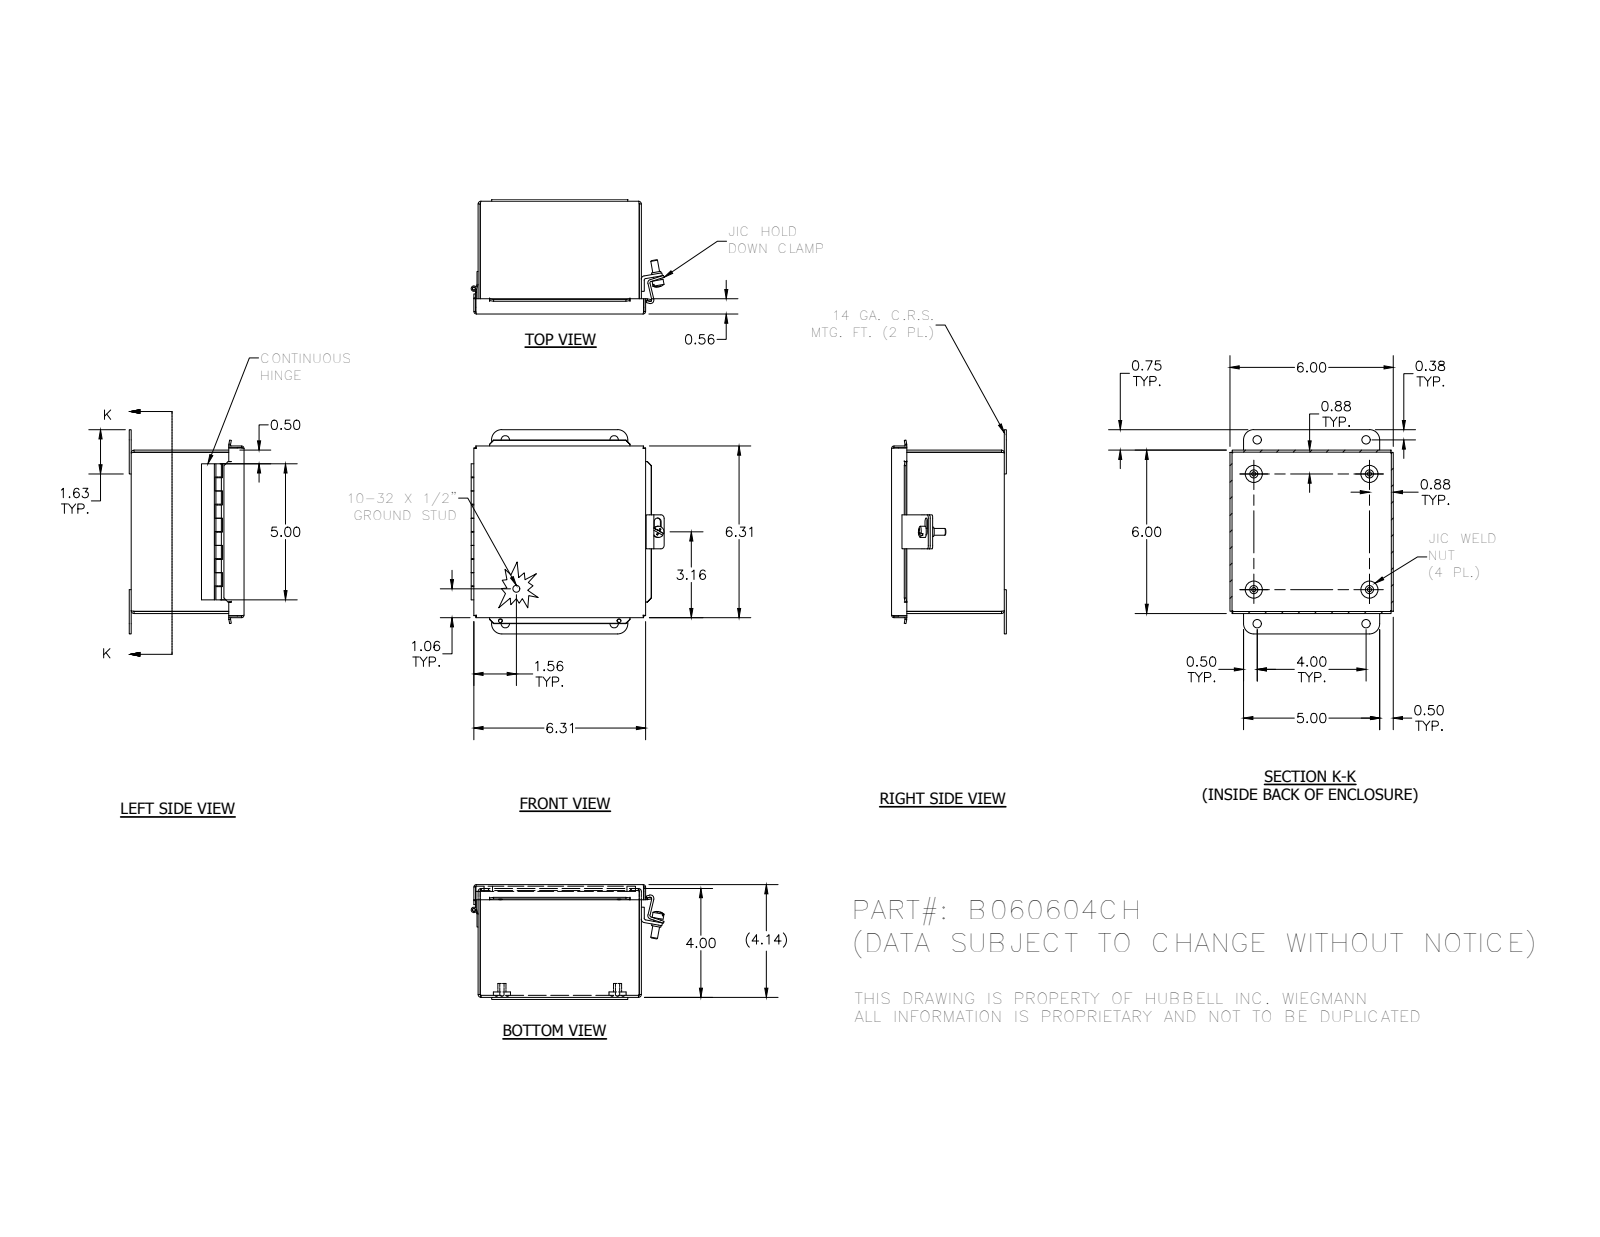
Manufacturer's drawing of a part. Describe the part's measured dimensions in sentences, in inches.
The part is named "B060604CH; 3499; 3482; C1001 (+8 more)". Its 3-D file was written by "Autodesk Inventor 2012 (AUTOMOTIVE_DESIGN)". It is 17 solids with 386 faces: 253 planar, 91 cylindrical and 42 other. Overall it measures 7.5 by 7.087 by 4.219 inches. Its volume is 18.05 cubic inches and its surface area 488.3 square inches. Round holes: 4 of diameter 0.156, 4 of diameter 0.31, 2 of diameter 0.14, 1 of diameter 0.116, 1 of diameter 0.196. Round bosses or shafts: 4 of diameter 0.625, 4 of diameter 0.3, 2 of diameter 0.25, 1 of diameter 0.41, 1 of diameter 0.344, 1 of diameter 0.2, 1 of diameter 0.19, 1 of diameter 0.1. Partial cylindrical surfaces (rounded edges, fillets, slot ends): 15 of radius 0.031, 8 of radius 0.105, 7 of radius 0.093, 4 of radius 0.125, 4 of radius 0.375, 3 of radius 0.063, 3 of radius 0.126, 2 of radius 0.133. The main face-to-face distances are 0.074, 5.926, 4.083, 6, 5.852, 4.144, 0.062, 4.009, 4.07, 0.075. The hole center spacings are 4.31, 1.256, 1.257, 4, 4.25, 5.502, 5.502, 6.01.
